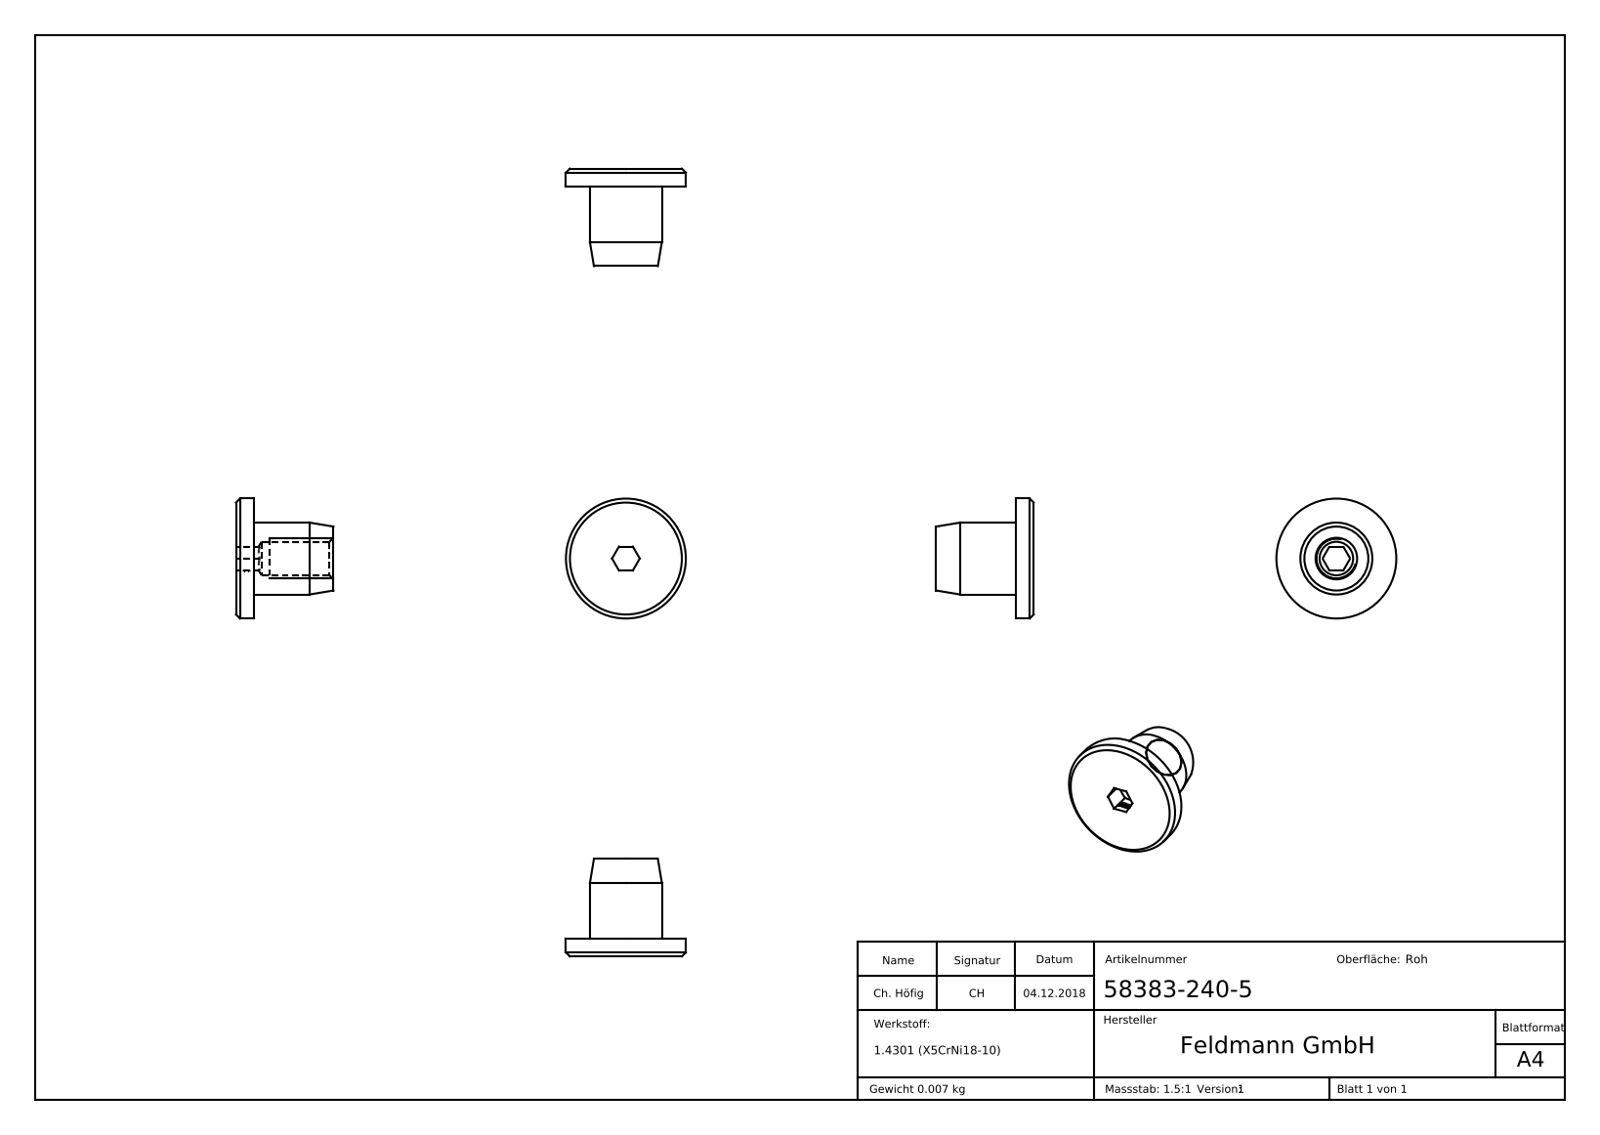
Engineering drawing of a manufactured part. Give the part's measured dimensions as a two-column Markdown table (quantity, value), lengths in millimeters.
| quantity | value |
| --- | --- |
| part name | 58383-240-5 |
| STEP written by | SolidWorks 2015 (CONFIG_CONTROL_DESIGN) |
| units | millimeters |
| bodies | 1 solid, 291 faces (136 planar, 6 cylindrical, 149 other) |
| overall size | 15 × 15 × 12.2 |
| volume | 846 mm³ |
| surface area | 841 mm² |
| round holes (diameter × count) | 4.2 × 1 |
| round bosses / shafts (diameter × count) | 15 × 1, 9 × 1 |
| main face-to-face distances | 2.2, 10, 12.2, 3, 3.1, 0.5, 0.48, 0.52, 0.65, 0.45 |
